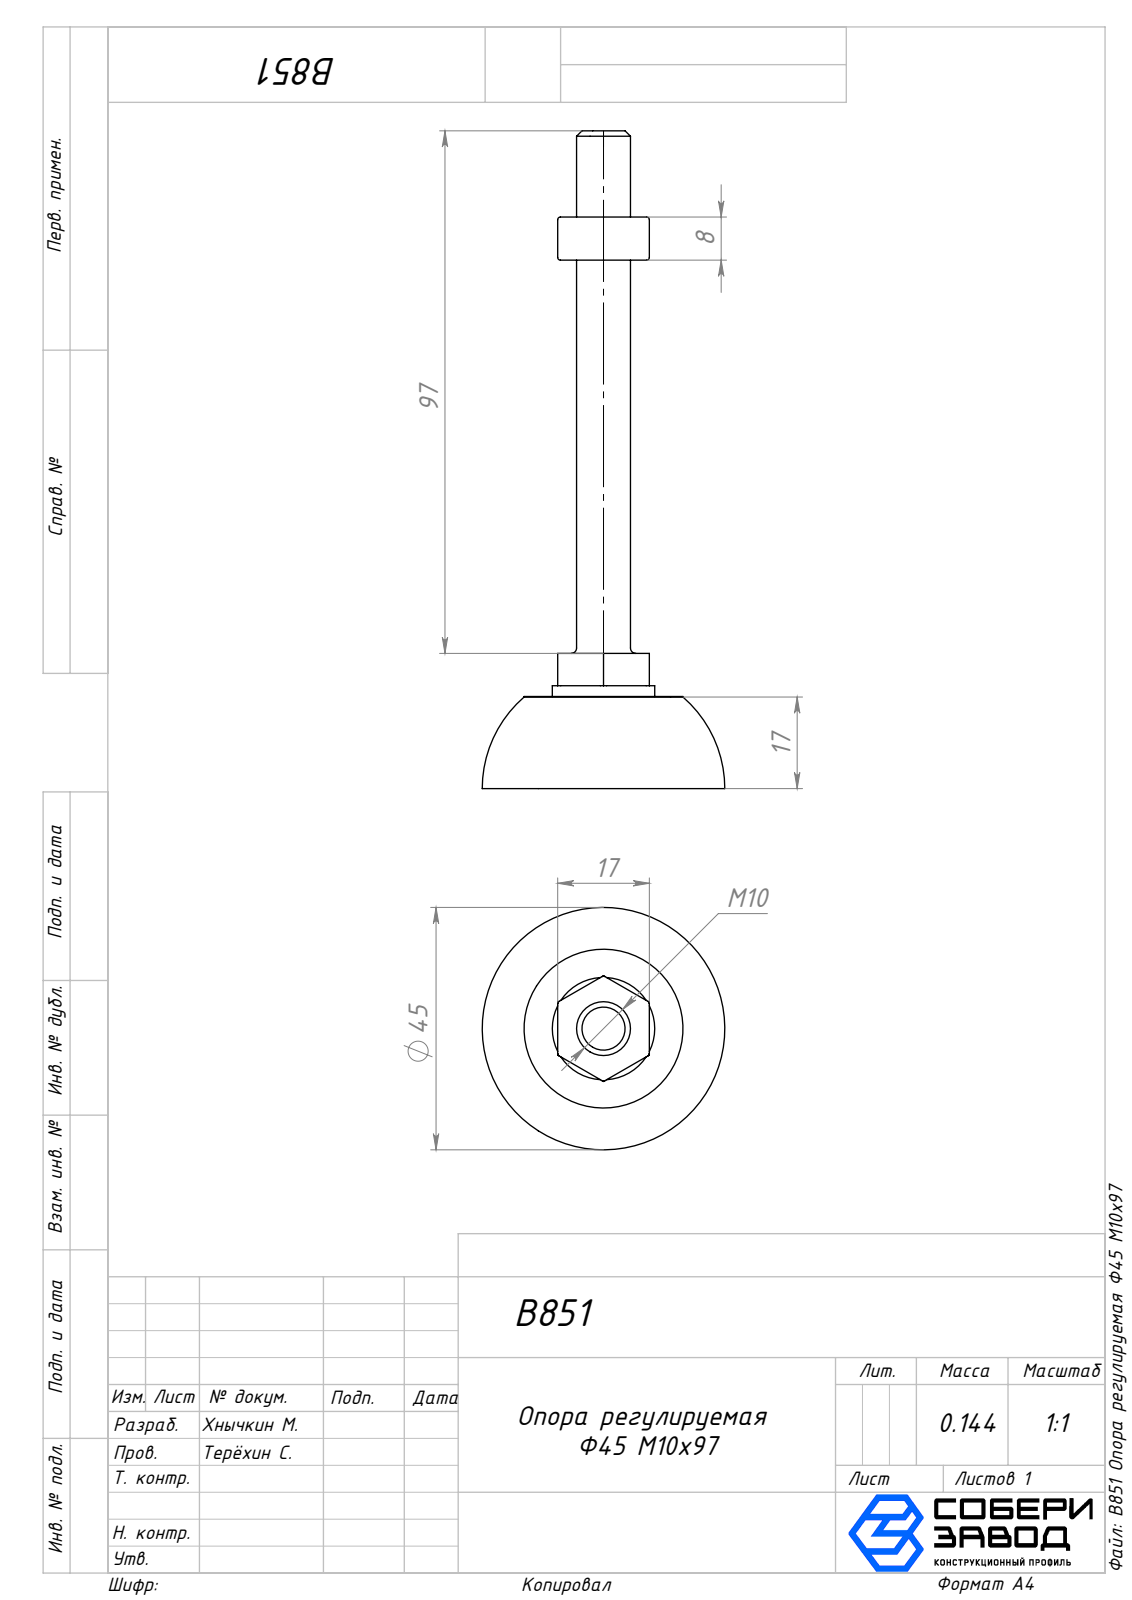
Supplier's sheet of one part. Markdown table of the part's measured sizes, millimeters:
| quantity | value |
| --- | --- |
| part name | B851 Опора регулируемая Ф45 М10х97; Опора_00; Мал. гайка_00; Гайка_00 (+1 more) |
| STEP written by | SolidWorks 2025 (AUTOMOTIVE_DESIGN) |
| units | millimeters |
| bodies | 4 solids, 131 faces (41 planar, 50 cylindrical, 40 other) |
| overall size | 122.1 × 45 × 45 |
| volume | 20 564 mm³ |
| surface area | 11 251 mm² |
| round holes (diameter × count) | 4 × 1, 5 × 1, 8 × 1 |
| round bosses / shafts (diameter × count) | 29.48 × 1, 19 × 1, 10 × 1 |
| partial cylindrical surfaces (radius × count) | 0.5 × 36 |
| main face-to-face distances | 17.1, 17, 8, 81, 16.9, 106.1, 89.2, 89, 98.1, 81.2 |
